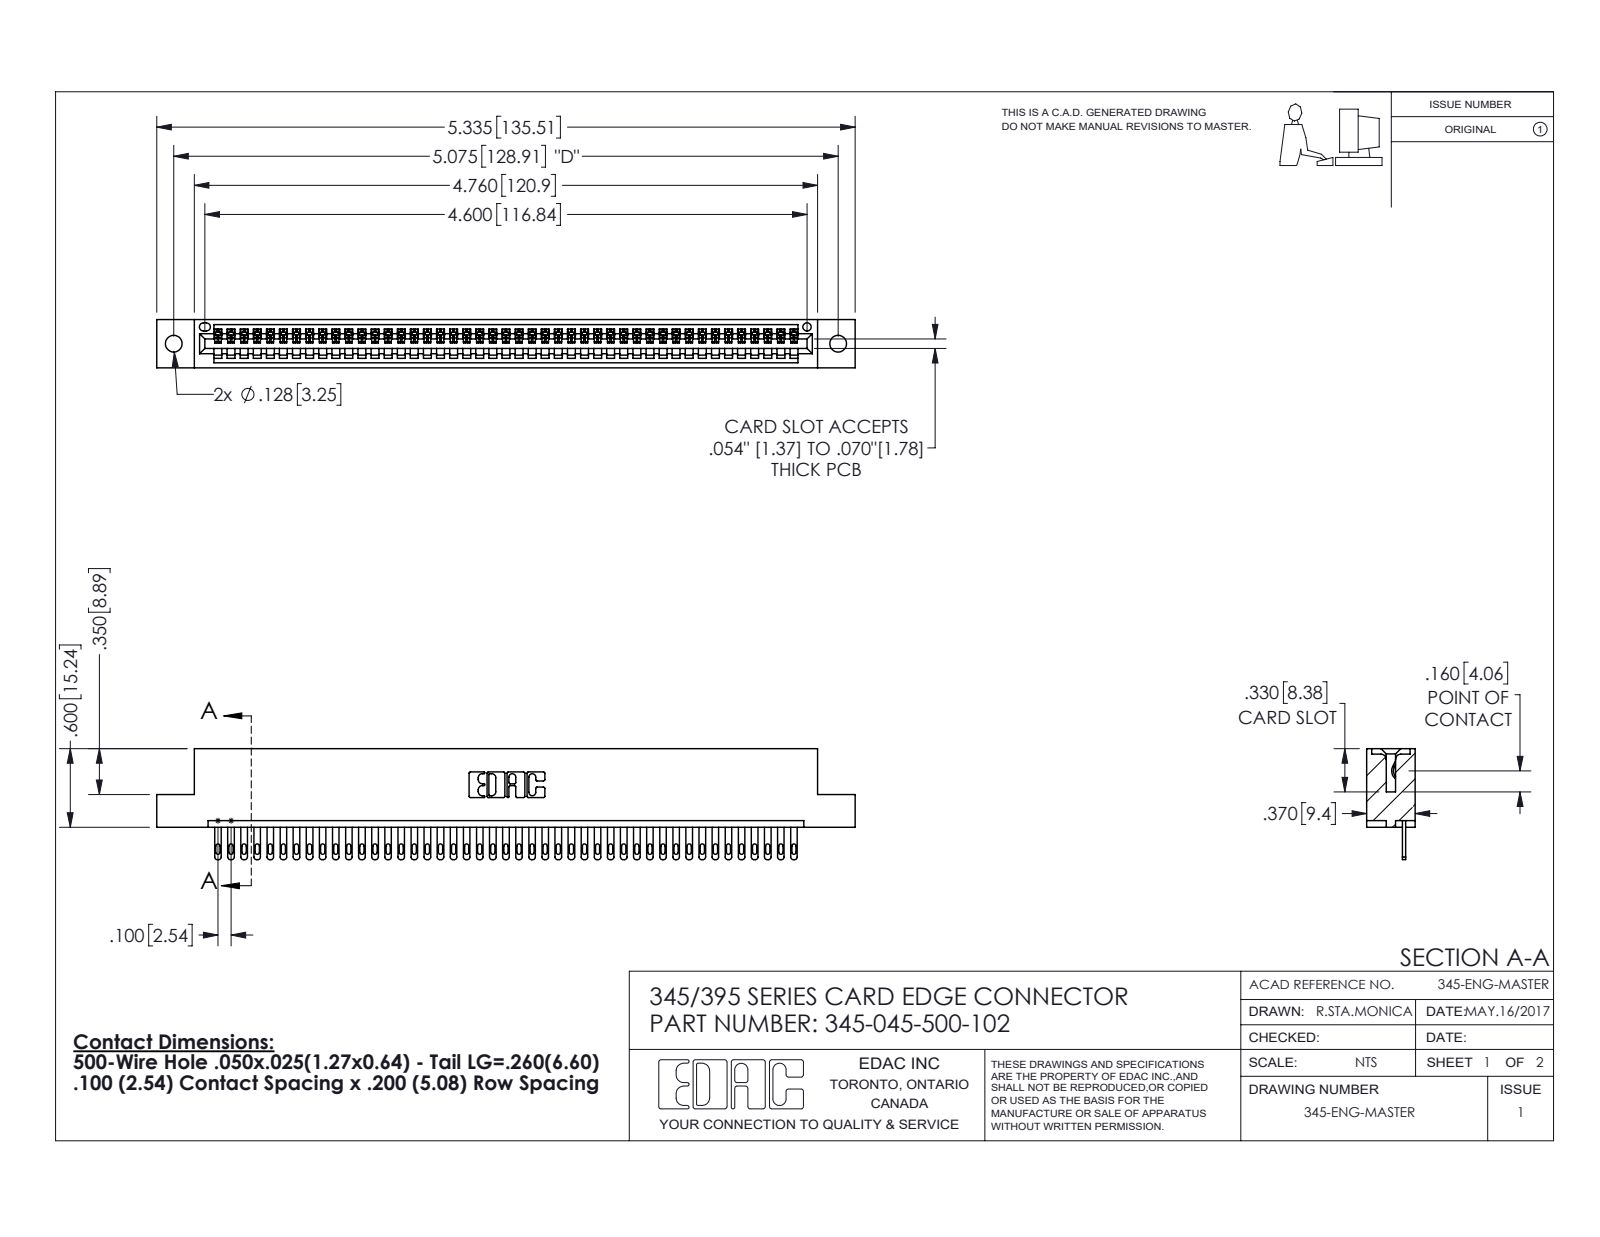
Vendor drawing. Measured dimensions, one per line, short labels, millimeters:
name: 345 Part_Flush Mounting Lugs - 0.128 Dia; 345-045-500-102; 345-292-001_345-293-100
written by: SolidWorks 2016 (CONFIG_CONTROL_DESIGN)
unit: mm
bodies: 46 solids, 2556 faces (1610 planar, 946 cylindrical, 0 other)
size: 135.5 × 21.5 × 9.4
volume: 12 900 mm³; area: 16 990 mm²
holes: 2× ⌀3.3, 1× ⌀1.6
rounds: 90× R0.2, 90× R0.4, 90× R0.5, 22× R0.3, 6× R0.2, 6× R0.8, 3× R0.7, 2× R0.8
face distances: 7.6, 1.8, 9.4, 5.1, 2.5, 6.9, 0.6, 5.7, 3.8, 1.8
hole spacings: 6.9, 122.9, 128.9
